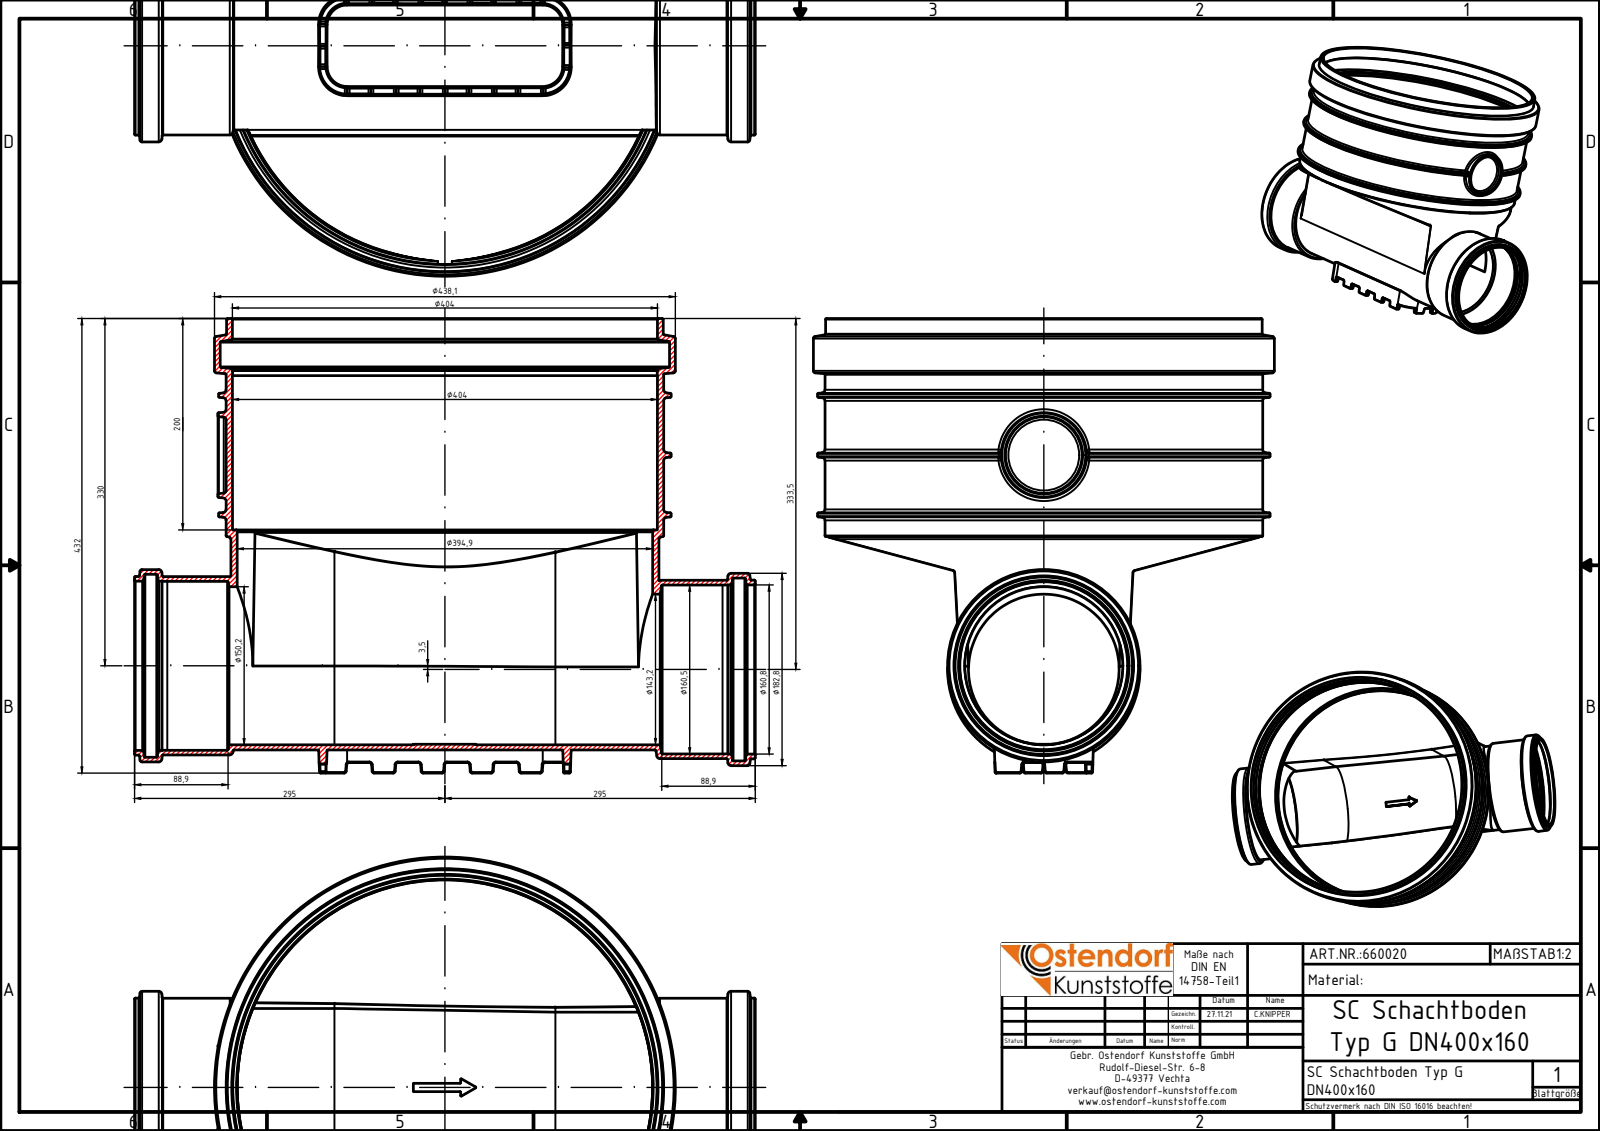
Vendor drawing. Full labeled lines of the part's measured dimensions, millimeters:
Part name (STEP PRODUCT): 660020 SC Schachtboden Typ G DN_OD 400_160
STEP written by: Autodesk Inventor 2020 (AUTOMOTIVE_DESIGN)
Units: millimetres
Bodies: 1 solid, 545 faces (81 planar, 170 cylindrical, 294 other)
Overall size (bounding box): 590 × 438.1 × 432
Volume: 4 660 000 mm³ · Surface area: 1 435 000 mm²
Round holes (diameter × count): ⌀160.5 ×2, ⌀160.8 ×2, ⌀173.8 ×2, ⌀143.2 ×1, ⌀150.2 ×1, ⌀394.9 ×1, ⌀404 ×1, ⌀427.1 ×1
Round bosses / shafts (diameter × count): ⌀182.8 ×2, ⌀169.8 ×2, ⌀169.5 ×2, ⌀438.1 ×1, ⌀430 ×1, ⌀416 ×1, ⌀415 ×1, ⌀406.9 ×1
Partial cylindrical surfaces — rounded edges, fillets, slot ends (radius × count): R1 ×56, R2 ×50, R0.5 ×7
Main face-to-face distances: 85.91, 200.88, 221.12, 422, 87, 590, 503, 10, 231.12, 432
Hole centre spacings: 3.5
